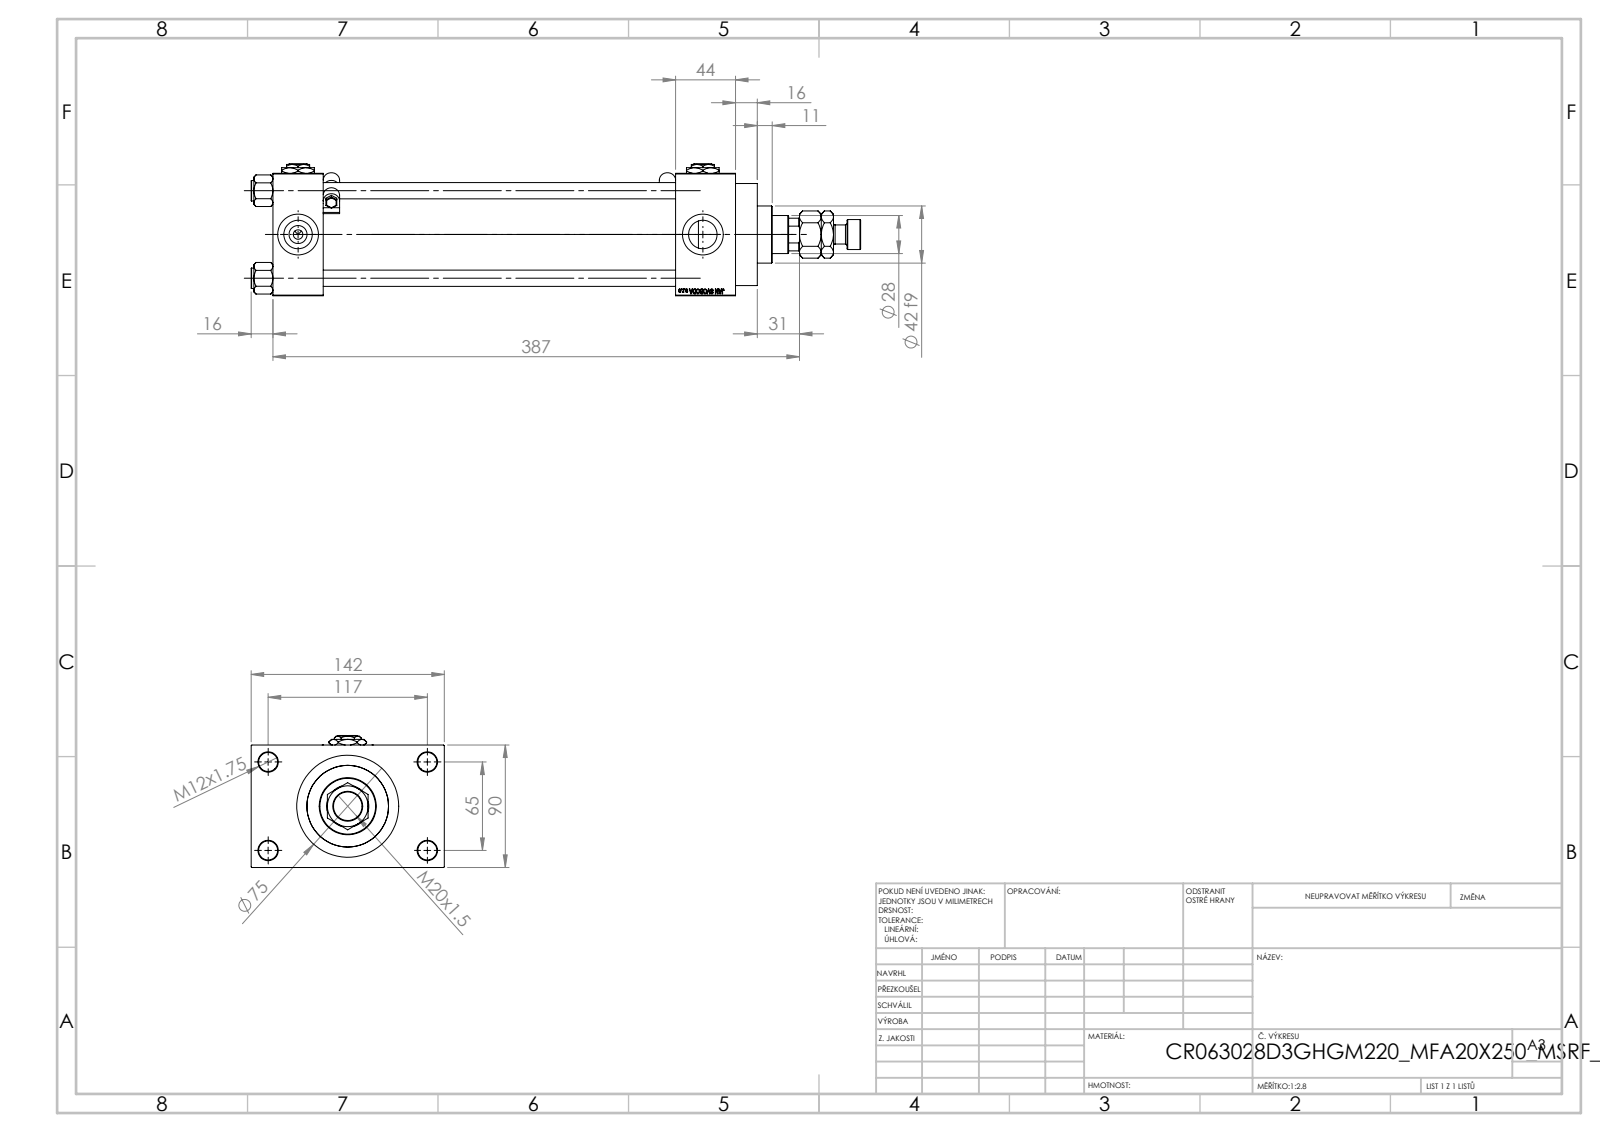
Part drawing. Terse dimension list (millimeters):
name: V215CR_VCP_D; V215_VC_A; V215CR_D_Body; MSRF_MSRG1 (+4 more)
written by: SolidWorks 2019 (CONFIG_CONTROL_DESIGN)
unit: mm
bodies: 16 solids, 1320 faces (597 planar, 131 cylindrical, 592 other)
size: 448 × 142 × 97
volume: 1 461 000 mm³; area: 345 716 mm²
holes: 4× ⌀12, 4× ⌀14, 4× ⌀20.96, 4× ⌀30, 3× ⌀7, 1× ⌀18.5, 1× ⌀28, 1× ⌀31, 1× ⌀50, 1× ⌀60, 1× ⌀63
bosses: 4× ⌀15, 2× ⌀5, 2× ⌀2.5, 1× ⌀75, 1× ⌀69, 1× ⌀42, 1× ⌀22, 1× ⌀14
rounds: 12× R0.5, 4× R6, 1× R13.5
face distances: 90, 259, 37, 296, 303, 340, 44, 116, 26, 356
hole spacings: 26.35, 45.47, 64.3, 66.92, 69.81, 90.65, 111.34, 65
